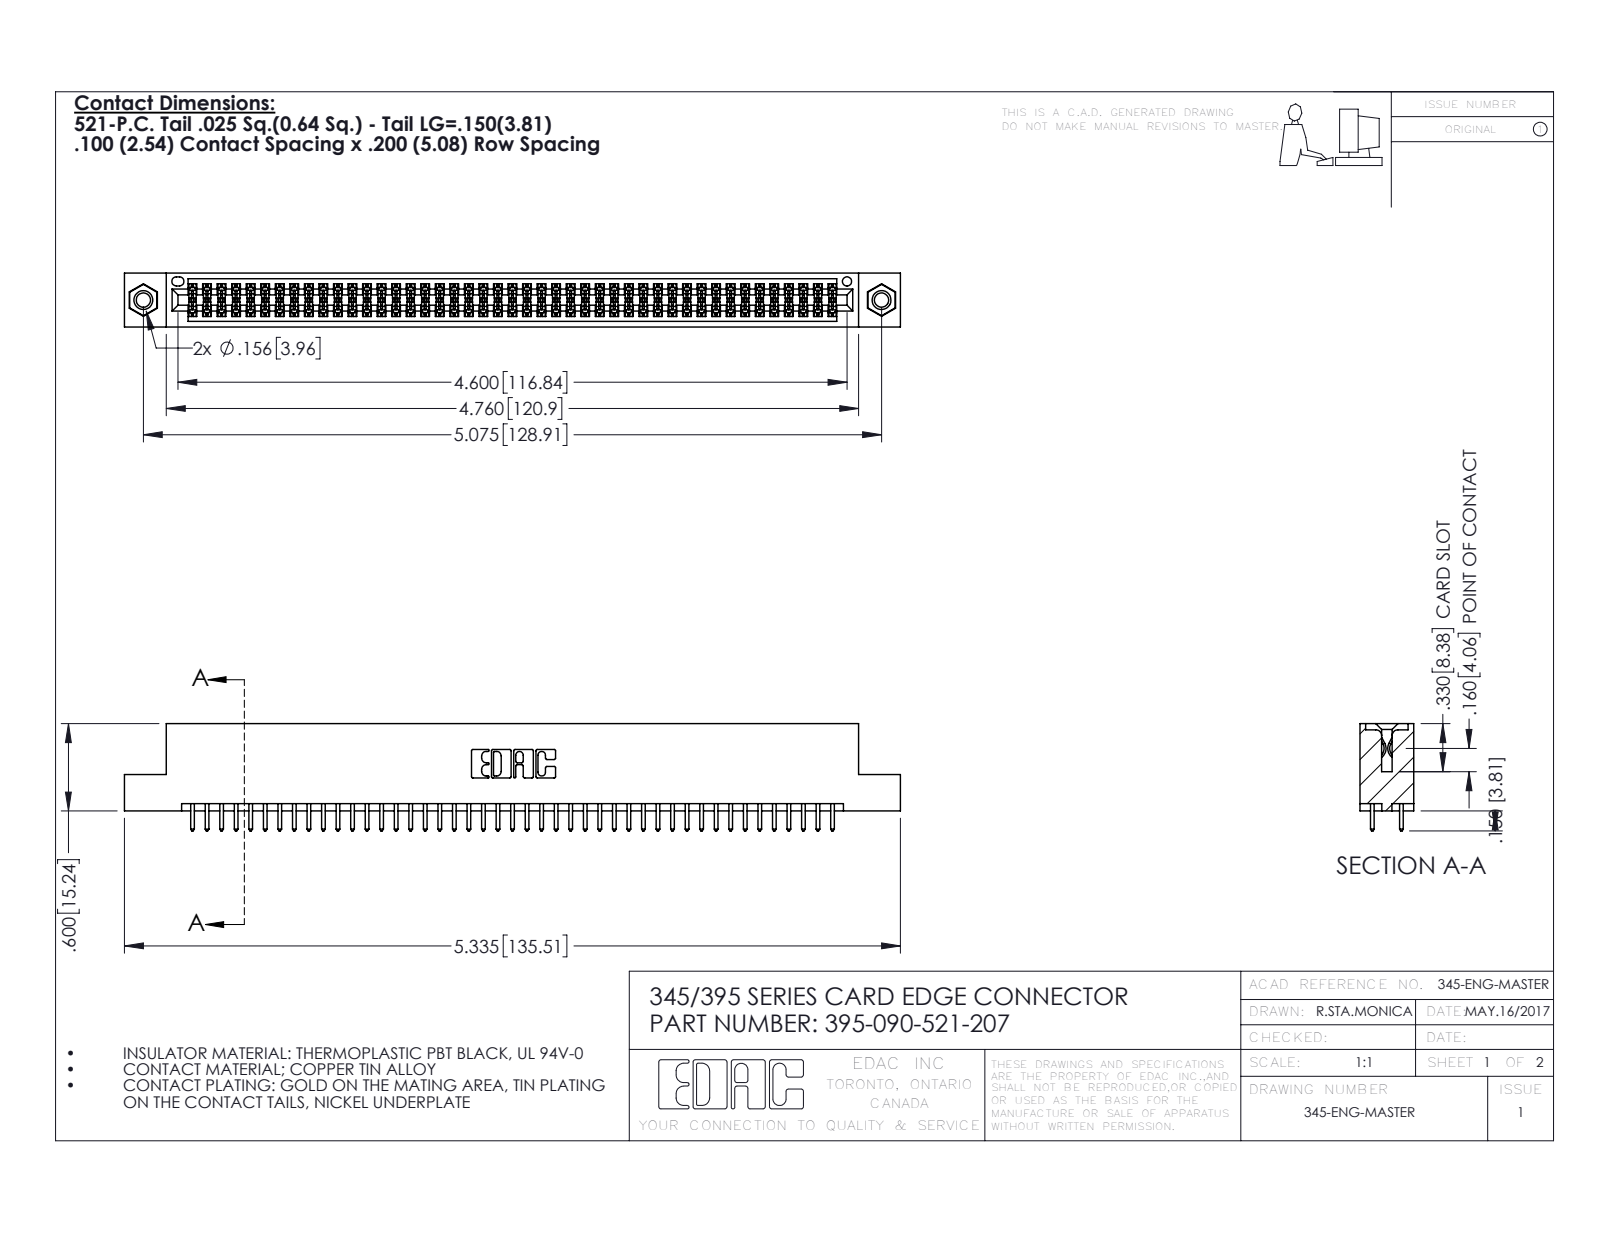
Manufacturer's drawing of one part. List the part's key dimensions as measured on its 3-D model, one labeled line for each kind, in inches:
Part name (STEP PRODUCT): 345 Part_Flush Mounting Lugs - 0.156 Dia-TI; 345-292-001_345-293-121; 395-090-521-207; 345-250-001_345-250-005-103
STEP written by: SolidWorks 2016 (CONFIG_CONTROL_DESIGN)
Units: inches
Bodies: 93 solids, 4686 faces (3082 planar, 1588 cylindrical, 16 other)
Overall size (bounding box): 5.335 × 0.737 × 0.37
Volume: 0.802 in³ · Surface area: 29.87 in²
Round holes (diameter × count): ⌀0.098 ×2, ⌀0.125 ×2, ⌀0.156 ×2, ⌀0.064 ×1
Round bosses / shafts (diameter × count): ⌀0.155 ×2
Partial cylindrical surfaces — rounded edges, fillets, slot ends (radius × count): R0.006 ×135, R0.01 ×90, R0.01 ×22, R0.007 ×6, R0.031 ×6, R0.026 ×3, R0.014 ×2, R0.019 ×2
Main face-to-face distances: 0.072, 0.298, 0.2, 0.37, 0.098, 0.272, 0.025, 0.225, 0.175, 0.149
Hole centre spacings: 0.27, 4.839, 5.075
